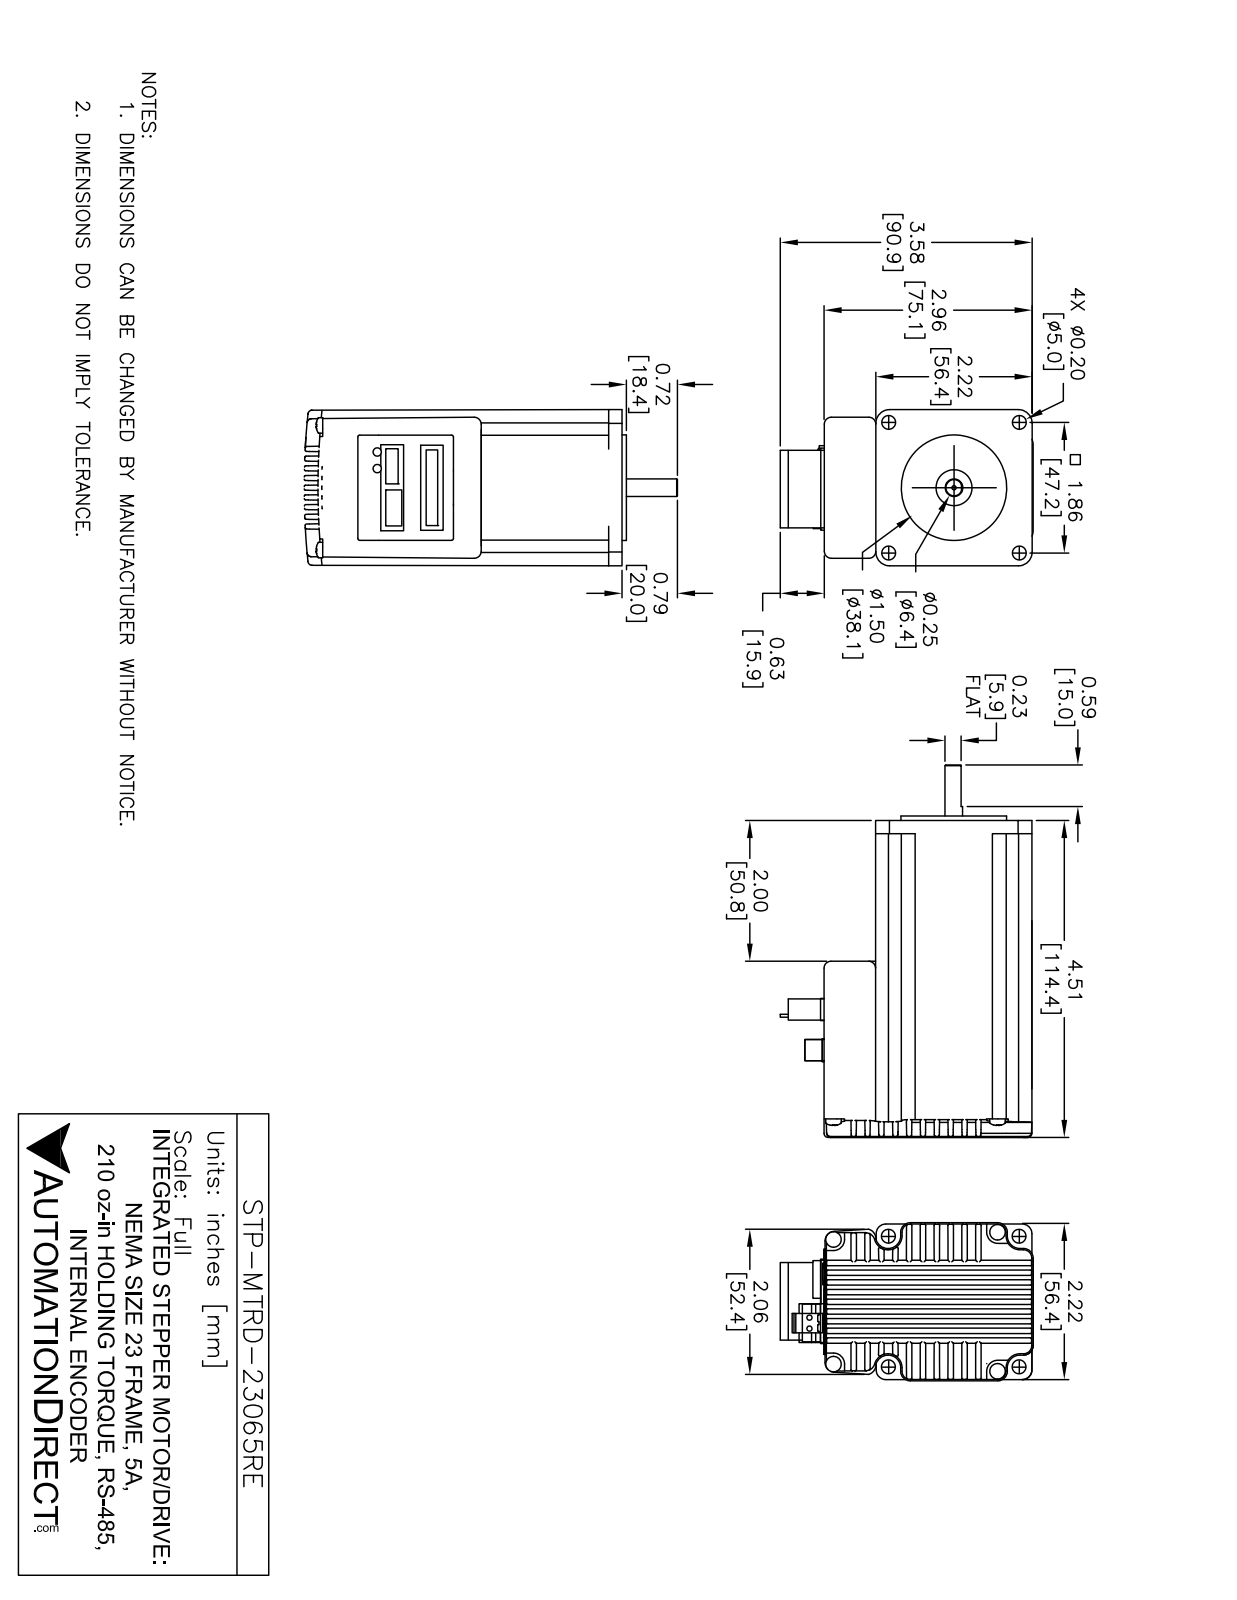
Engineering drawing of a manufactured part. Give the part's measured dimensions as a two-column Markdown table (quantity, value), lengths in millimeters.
| quantity | value |
| --- | --- |
| part name | STP-MTRD-23065RE |
| STEP written by | SolidWorks 2018 (AUTOMOTIVE_DESIGN) |
| units | millimeters |
| bodies | 1 solid, 140 faces (58 planar, 55 cylindrical, 27 other) |
| overall size | 134.4 × 82.05 × 56.4 |
| volume | 387 214 mm³ |
| surface area | 37 800 mm² |
| round holes (diameter × count) | 5 × 4, 1.5 × 1, 12.97 × 1 |
| round bosses / shafts (diameter × count) | 3.65 × 2, 38.1 × 1, 6.35 × 1 |
| partial cylindrical surfaces (radius × count) | 5 × 12, 1.5 × 9, 2.5 × 8, 4.64 × 4 |
| main face-to-face distances | 56.4, 75, 18.6, 114.4, 2, 54.4, 52.4, 116, 1.6, 63.6 |
| hole center spacings | 33.33, 47.14, 66.67 |
